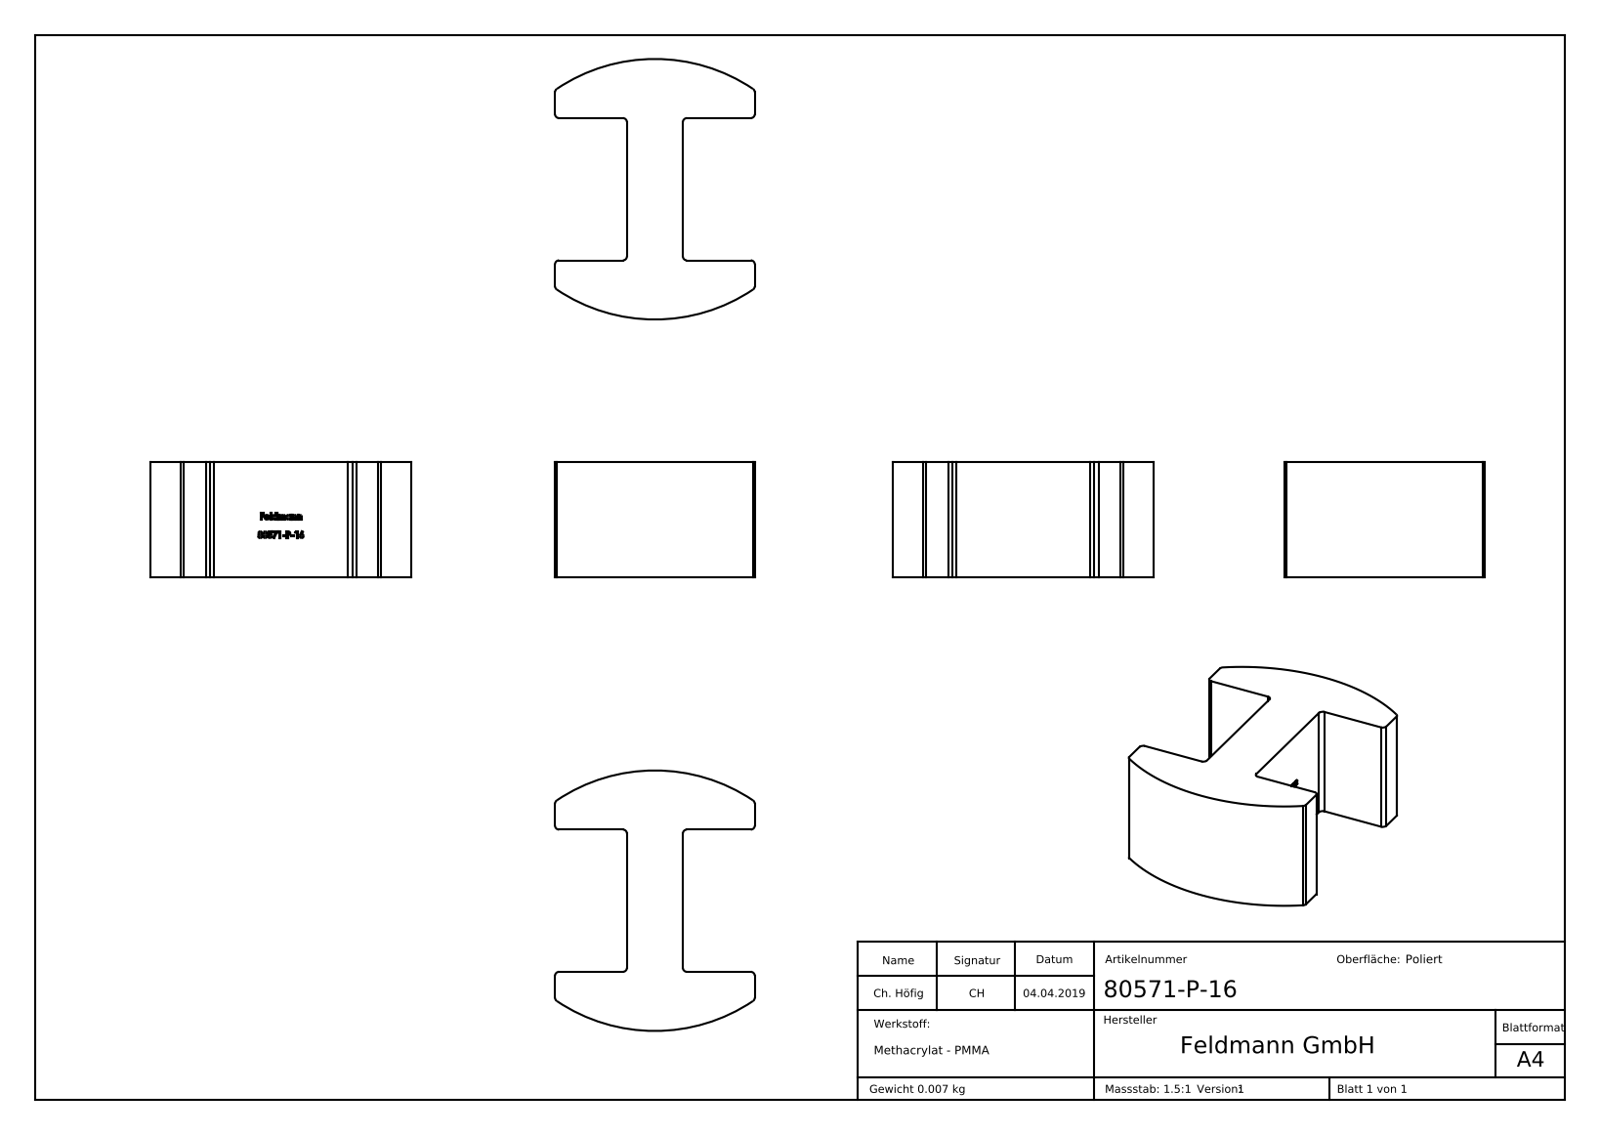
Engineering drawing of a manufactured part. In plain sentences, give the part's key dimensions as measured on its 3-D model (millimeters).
The part is named "80571-P-16". Its 3-D file was written by "SolidWorks 2015 (CONFIG_CONTROL_DESIGN)". It is 1 solid with 245 faces: 137 planar, 15 cylindrical and 93 other. Overall it measures 32.59 by 25 by 14.5 millimeters. Its volume is 6 262 cubic millimeters and its surface area 2 854 square millimeters. Partial cylindrical surfaces (rounded edges, fillets, slot ends): 12 of radius 0.5, 2 of radius 22. The main face-to-face distances are 14.5, 7, 17.8, 9, 16, 25, 9.1, 15.9, 6.9, 7.25.
